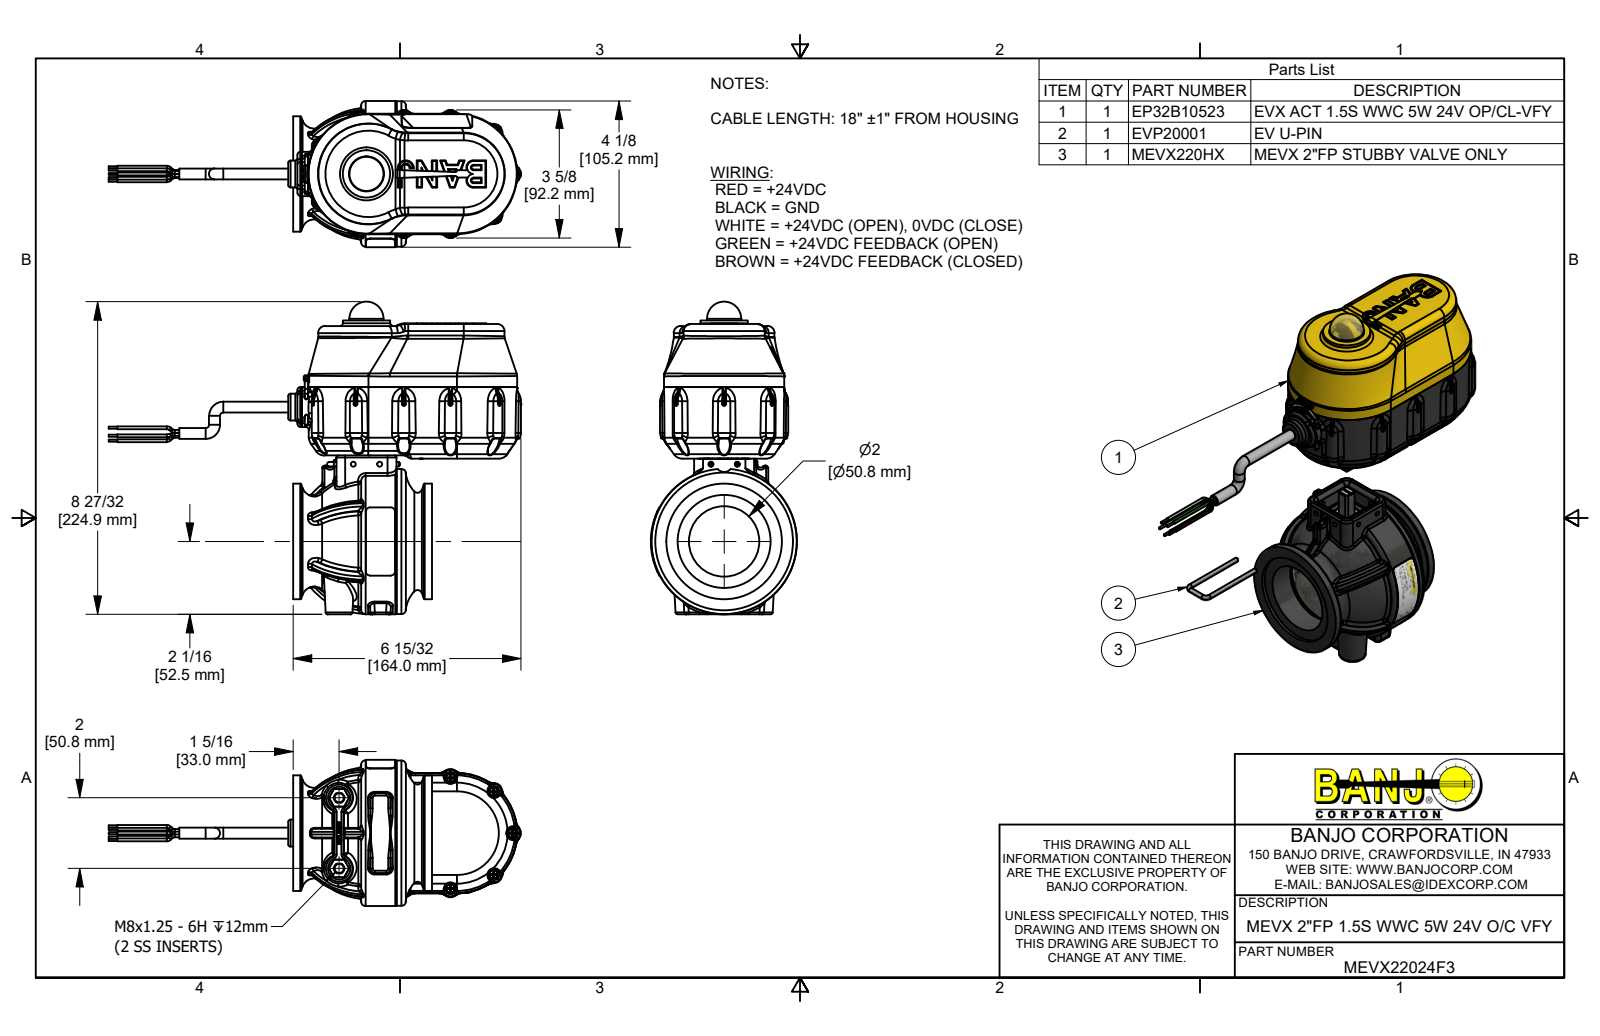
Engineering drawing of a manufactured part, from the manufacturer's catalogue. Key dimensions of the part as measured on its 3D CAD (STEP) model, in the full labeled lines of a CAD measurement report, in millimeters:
Part name (STEP PRODUCT): MEVX22024F3; EP32B10523; B61905PPHS; B632038PM (+8 more)
STEP written by: Autodesk Inventor 2019 (AUTOMOTIVE_DESIGN)
Units: millimetres
Bodies: 84 solids, 10831 faces (2811 planar, 3111 cylindrical, 4909 other)
Overall size (bounding box): 296.8 × 224.9 × 105.2
Volume: 871 300 mm³ · Surface area: 392 800 mm²
Round holes (diameter × count): ⌀2.4 ×11, ⌀3.8 ×11, ⌀2 ×7, ⌀2.7 ×4, ⌀3.2 ×4, ⌀3.4 ×4, ⌀3.5 ×4, ⌀3.8 ×4, ⌀3.8 ×4, ⌀4.3 ×4, ⌀2.7 ×2, ⌀3 ×2
Round bosses / shafts (diameter × count): ⌀2 ×25, ⌀6.4 ×17, ⌀3.6 ×11, ⌀2.7 ×11, ⌀2.2 ×11, ⌀1.5 ×10, ⌀6.9 ×4, ⌀5.6 ×4
Partial cylindrical surfaces — rounded edges, fillets, slot ends (radius × count): R0.3 ×180, R1 ×145, R0.3 ×92, R0.5 ×71, R0.1 ×53, R0.8 ×34, R1.5 ×31, R2 ×28
Main face-to-face distances: 2.5, 65.2, 1.5, 5.4, 3.8, 42.8, 46.6, 48.2, 62.6, 19.8
Hole centre spacings: 32.6, 56.4, 38.4, 72.4, 96.2, 12.4, 17, 19.1
